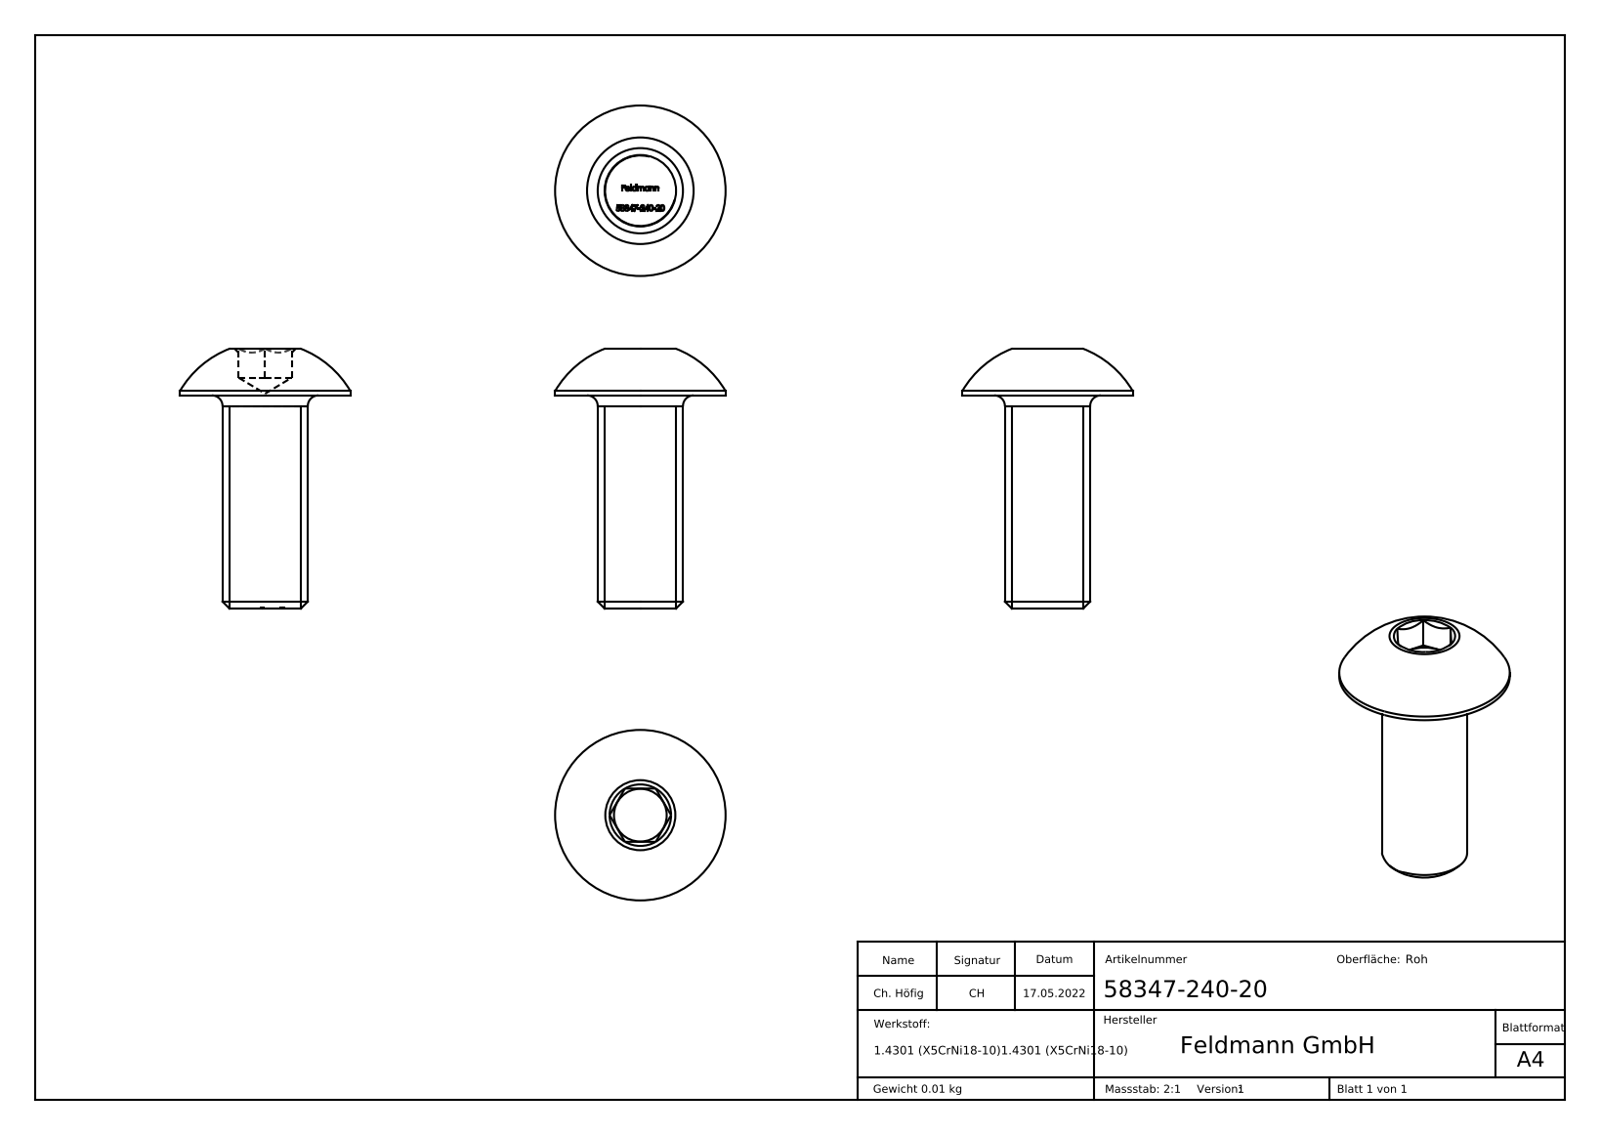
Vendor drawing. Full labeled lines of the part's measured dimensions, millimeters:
Part name (STEP PRODUCT): 58347-240-20
STEP written by: SolidWorks 2018 (CONFIG_CONTROL_DESIGN)
Units: millimetres
Bodies: 1 solid, 283 faces (154 planar, 2 cylindrical, 127 other)
Overall size (bounding box): 24.4 × 16 × 16
Volume: 1 520 mm³ · Surface area: 1 023 mm²
Round bosses / shafts (diameter × count): ⌀16 ×1, ⌀8 ×1
Main face-to-face distances: 20, 5, 4.4, 24.4, 1.65, 2.75, 21.65, 24.3, 21.55, 19.9
